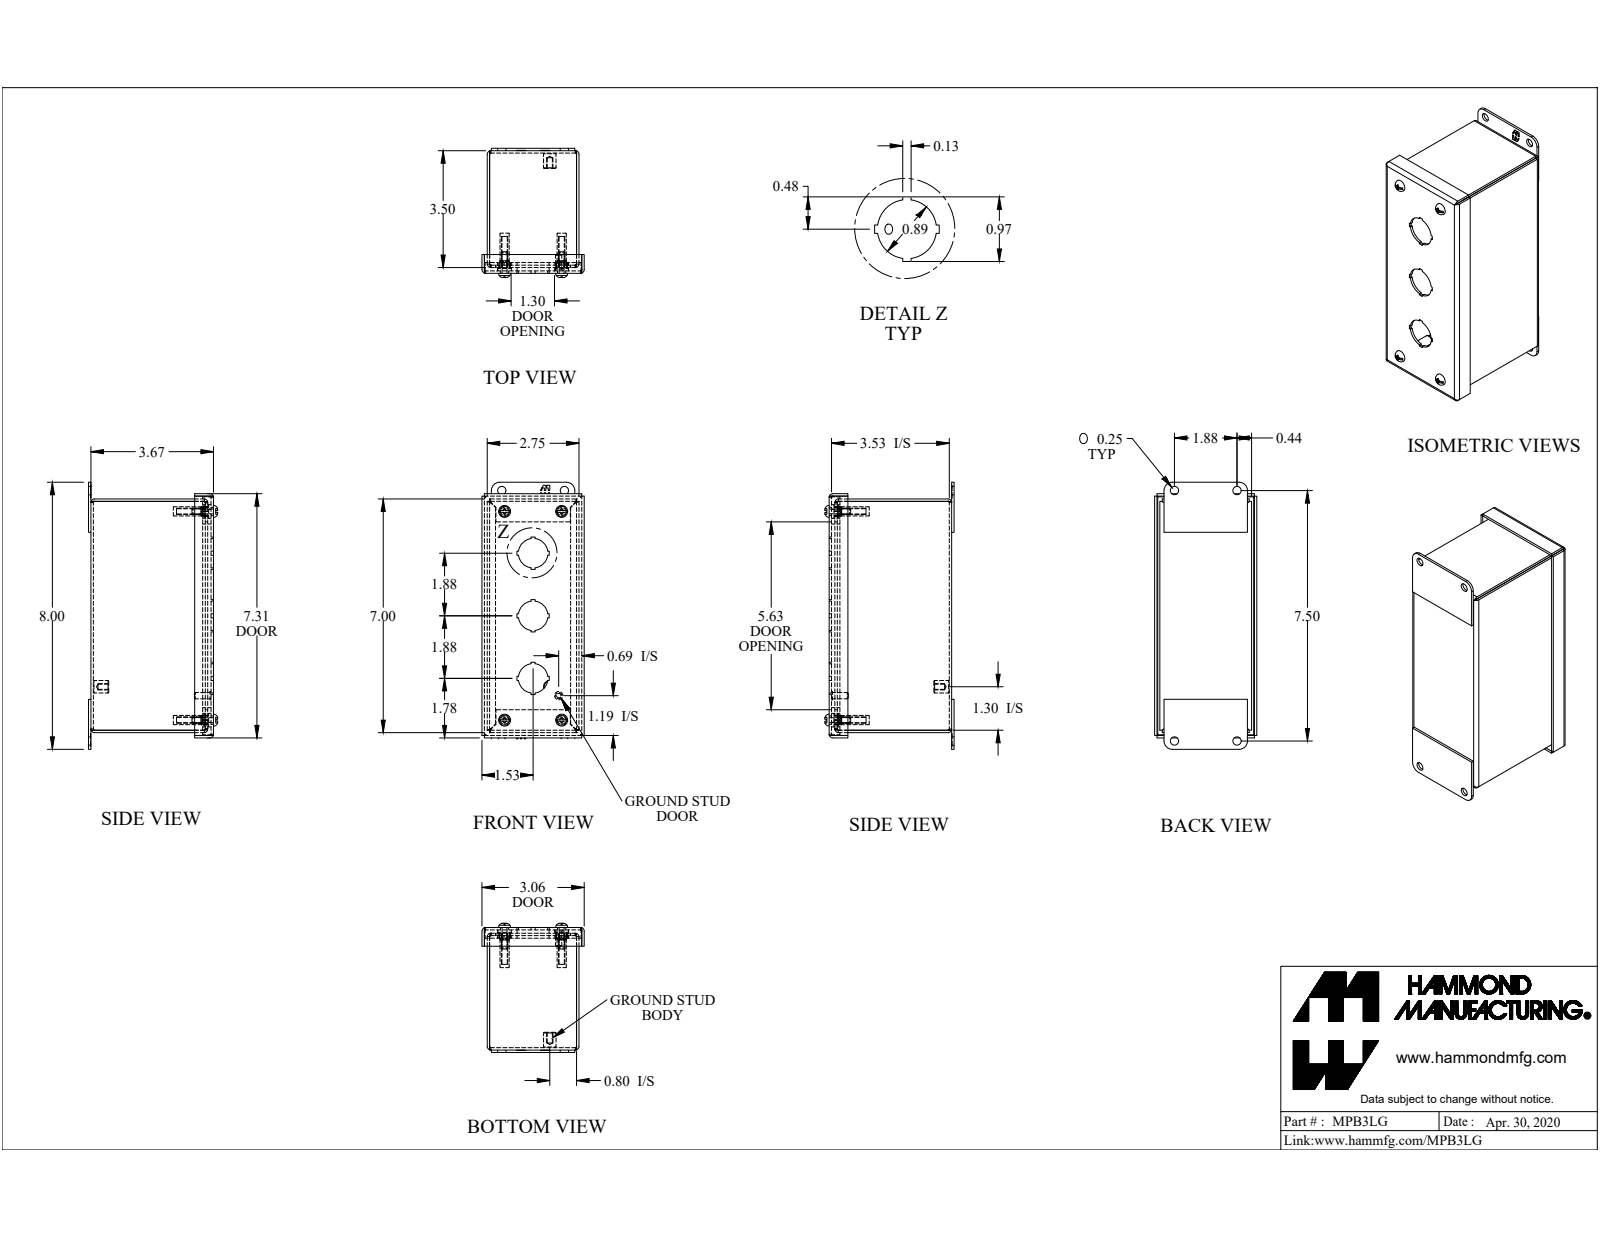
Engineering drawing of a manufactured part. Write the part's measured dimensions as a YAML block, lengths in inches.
part_name: "MPB3LG"
step_written_by: "SolidWorks 2019 (AUTOMOTIVE_DESIGN)"
units: inches
bodies: {solids: 19, faces: 539, planar: 395, cylindrical: 108, other: 36}
overall_size: [8, 3.871, 3.063]
volume: 11.14
surface_area: 293.7
round_holes:
  - {diameter: 0.25, count: 8}
  - {diameter: 0.159, count: 4}
  - {diameter: 0.406, count: 4}
  - {diameter: 0.886, count: 3}
  - {diameter: 0.156, count: 1}
round_bosses_or_shafts:
  - {diameter: 0.39, count: 4}
  - {diameter: 0.275, count: 4}
  - {diameter: 0.19, count: 4}
  - {diameter: 0.148, count: 4}
  - {diameter: 0.375, count: 1}
  - {diameter: 0.25, count: 1}
  - {diameter: 0.188, count: 1}
partial_cylinders:
  - {radius: 0.036, count: 12}
  - {radius: 0.108, count: 12}
  - {radius: 0.16, count: 4}
  - {radius: 0.171, count: 4}
  - {radius: 0.25, count: 4}
face_to_face_distances: [0.072, 0.072, 2.678, 3.6, 3.672, 2.75, 2.606, 3.528, 6.928, 0.172]
hole_center_spacings: [1.711, 0.63, 1.898, 3.241, 3.865, 6.25, 6.48, 6.876]
